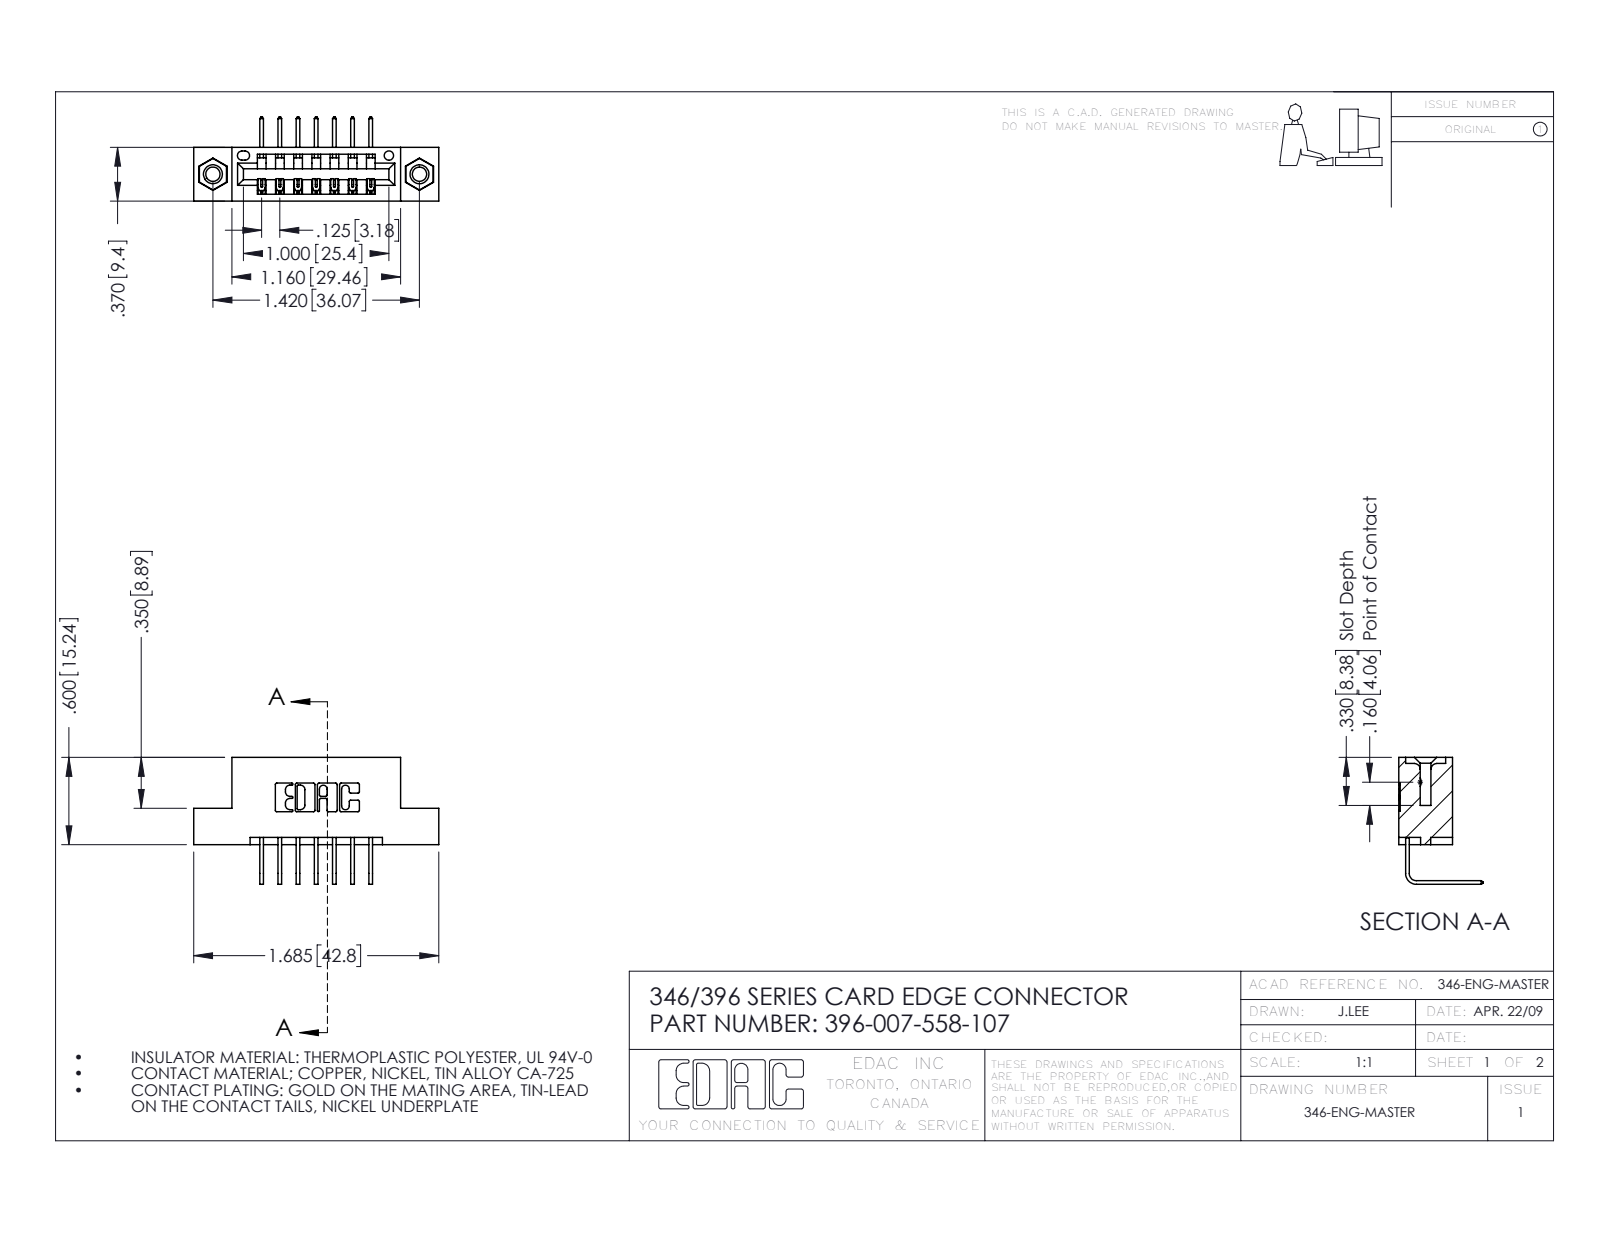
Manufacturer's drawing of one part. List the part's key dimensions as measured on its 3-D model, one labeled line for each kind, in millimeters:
Part name (STEP PRODUCT): 346 Part_Flush Mounting Lugs - 0.156 Dia-TI; 345-250-001_345-250-005-103; 396-007-558-107; 345-292-001_558 Tail - 2
STEP written by: SolidWorks 2016 (CONFIG_CONTROL_DESIGN)
Units: millimetres
Bodies: 10 solids, 602 faces (402 planar, 184 cylindrical, 16 other)
Overall size (bounding box): 42.8 × 22.2 × 14.7
Volume: 3 870 mm³ · Surface area: 4 628 mm²
Round holes (diameter × count): ⌀2.5 ×2, ⌀3.2 ×2, ⌀4 ×2, ⌀1.6 ×1
Round bosses / shafts (diameter × count): ⌀3.9 ×2
Partial cylindrical surfaces — rounded edges, fillets, slot ends (radius × count): R0.3 ×22, R0.2 ×14, R0.2 ×6, R0.8 ×6, R0.7 ×3, R0.8 ×2, R1 ×2, R0.4 ×1
Main face-to-face distances: 6.4, 9.4, 8.2, 1.2, 7.6, 0.6, 3.8, 5.6, 2.5, 4.4
Hole centre spacings: 6.2, 30.9, 36.1
